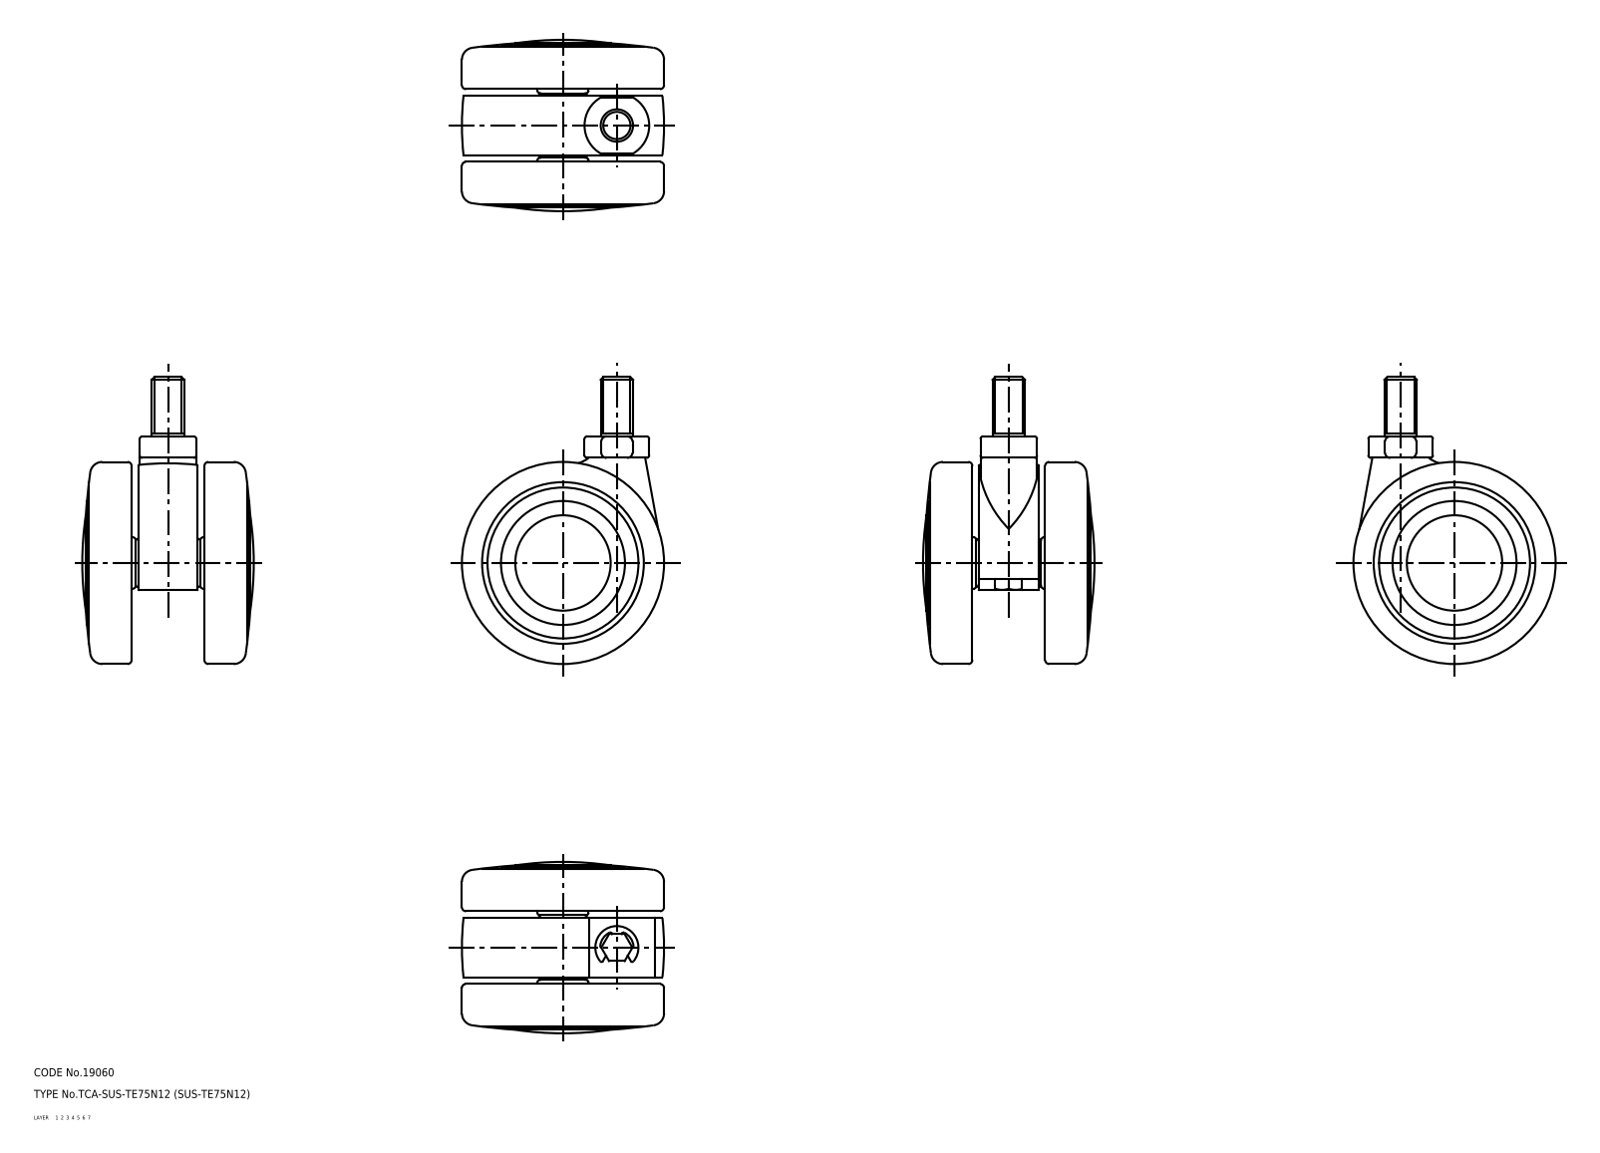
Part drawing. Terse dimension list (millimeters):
name: wheel_mr; wheel; main shaft; SUS_TE75N12_4652_36
written by: CADfix (AUTOMOTIVE_DESIGN)
unit: mm
bodies: 4 solids, 141 faces (0 planar, 0 cylindrical, 141 other)
size: 106.5 × 75 × 63.62
volume: 200 634 mm³; area: 48 227 mm²
